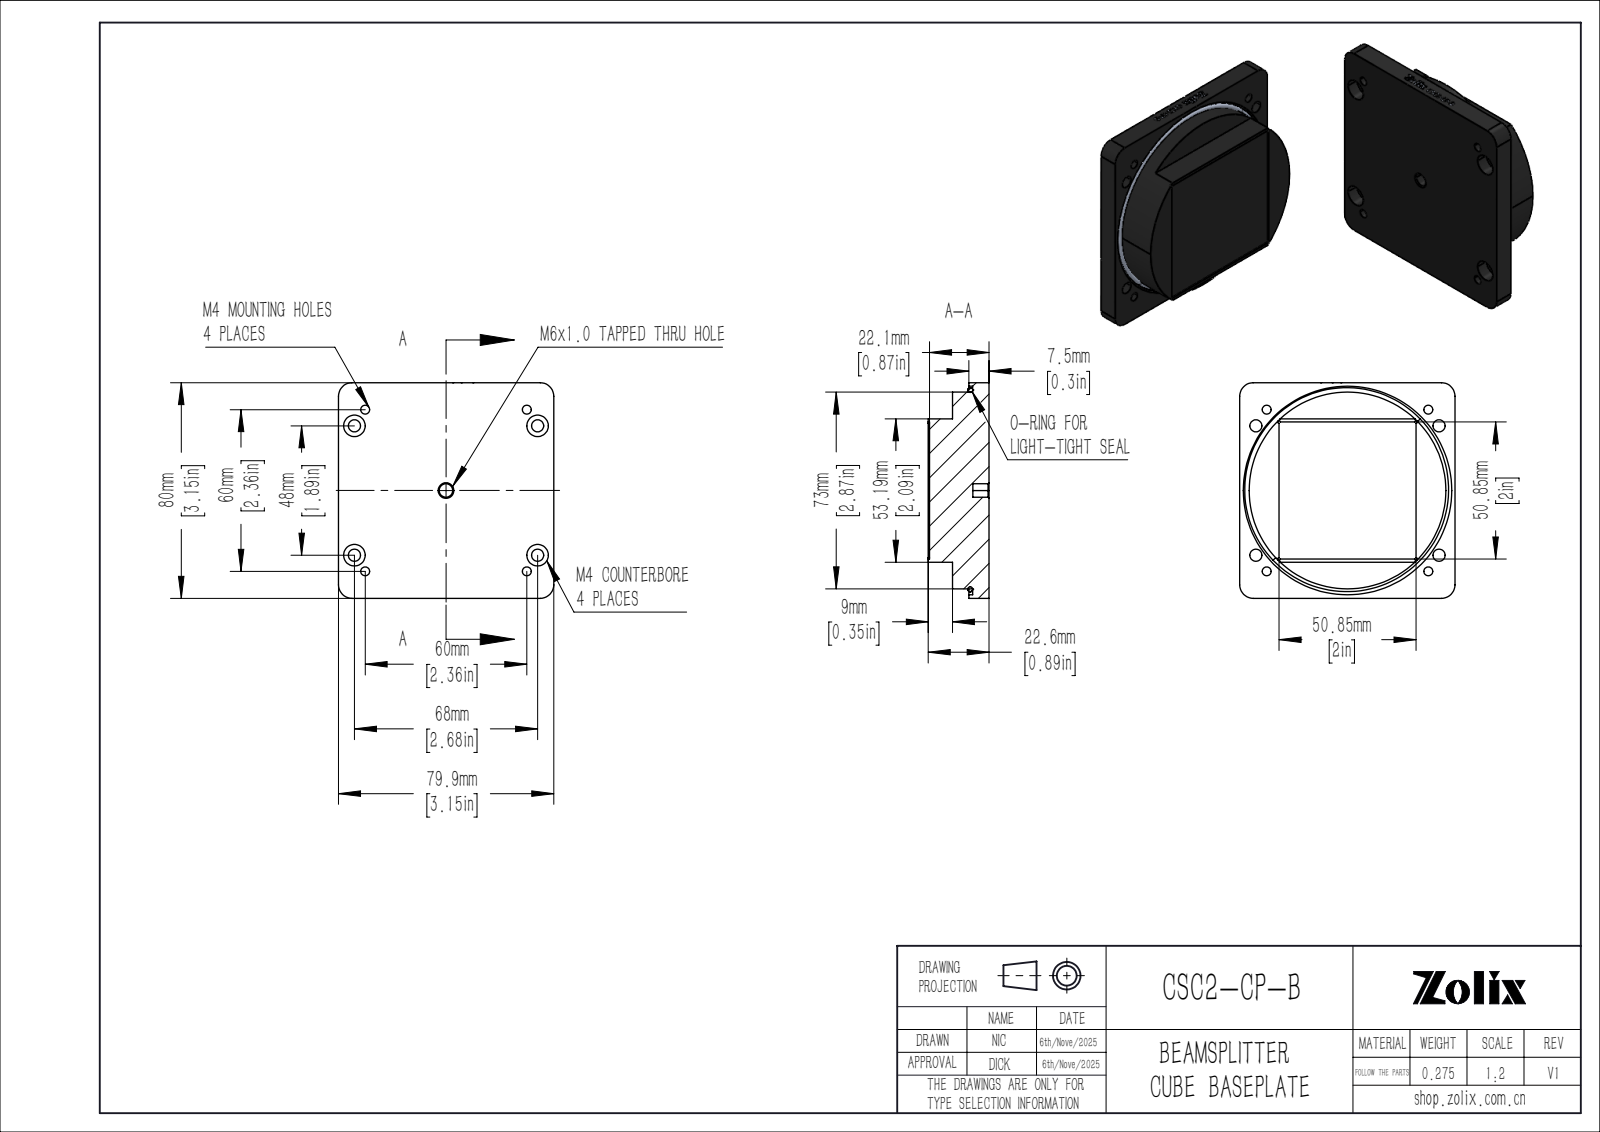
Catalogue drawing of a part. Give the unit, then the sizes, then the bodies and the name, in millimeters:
Units: millimetres
Overall size (bounding box): 80 × 79.9 × 22.6
Round holes (diameter × count): ⌀3.3 ×4, ⌀4.5 ×4, ⌀8 ×4, ⌀5 ×1, ⌀77.4 ×1
Round bosses / shafts (diameter × count): ⌀73 ×1
Partial cylindrical surfaces — rounded edges, fillets, slot ends (radius × count): R0.5 ×4, R5 ×4
Main face-to-face distances: 22.1, 7.5, 14.6, 6.1, 15.1, 0.5, 22.6, 9, 8.5, 13.6
Hole centre spacings: 7.21, 41.62, 42.43, 54.15, 60, 64.28, 83.74, 48
Volume: 101 936 mm³ · Surface area: 21 361 mm²
Bodies: 2 solids, 355 faces (231 planar, 40 cylindrical, 84 other)
Part name (STEP PRODUCT): CSC2-CP-B
STEP written by: SolidWorks 2020 (CONFIG_CONTROL_DESIGN)
